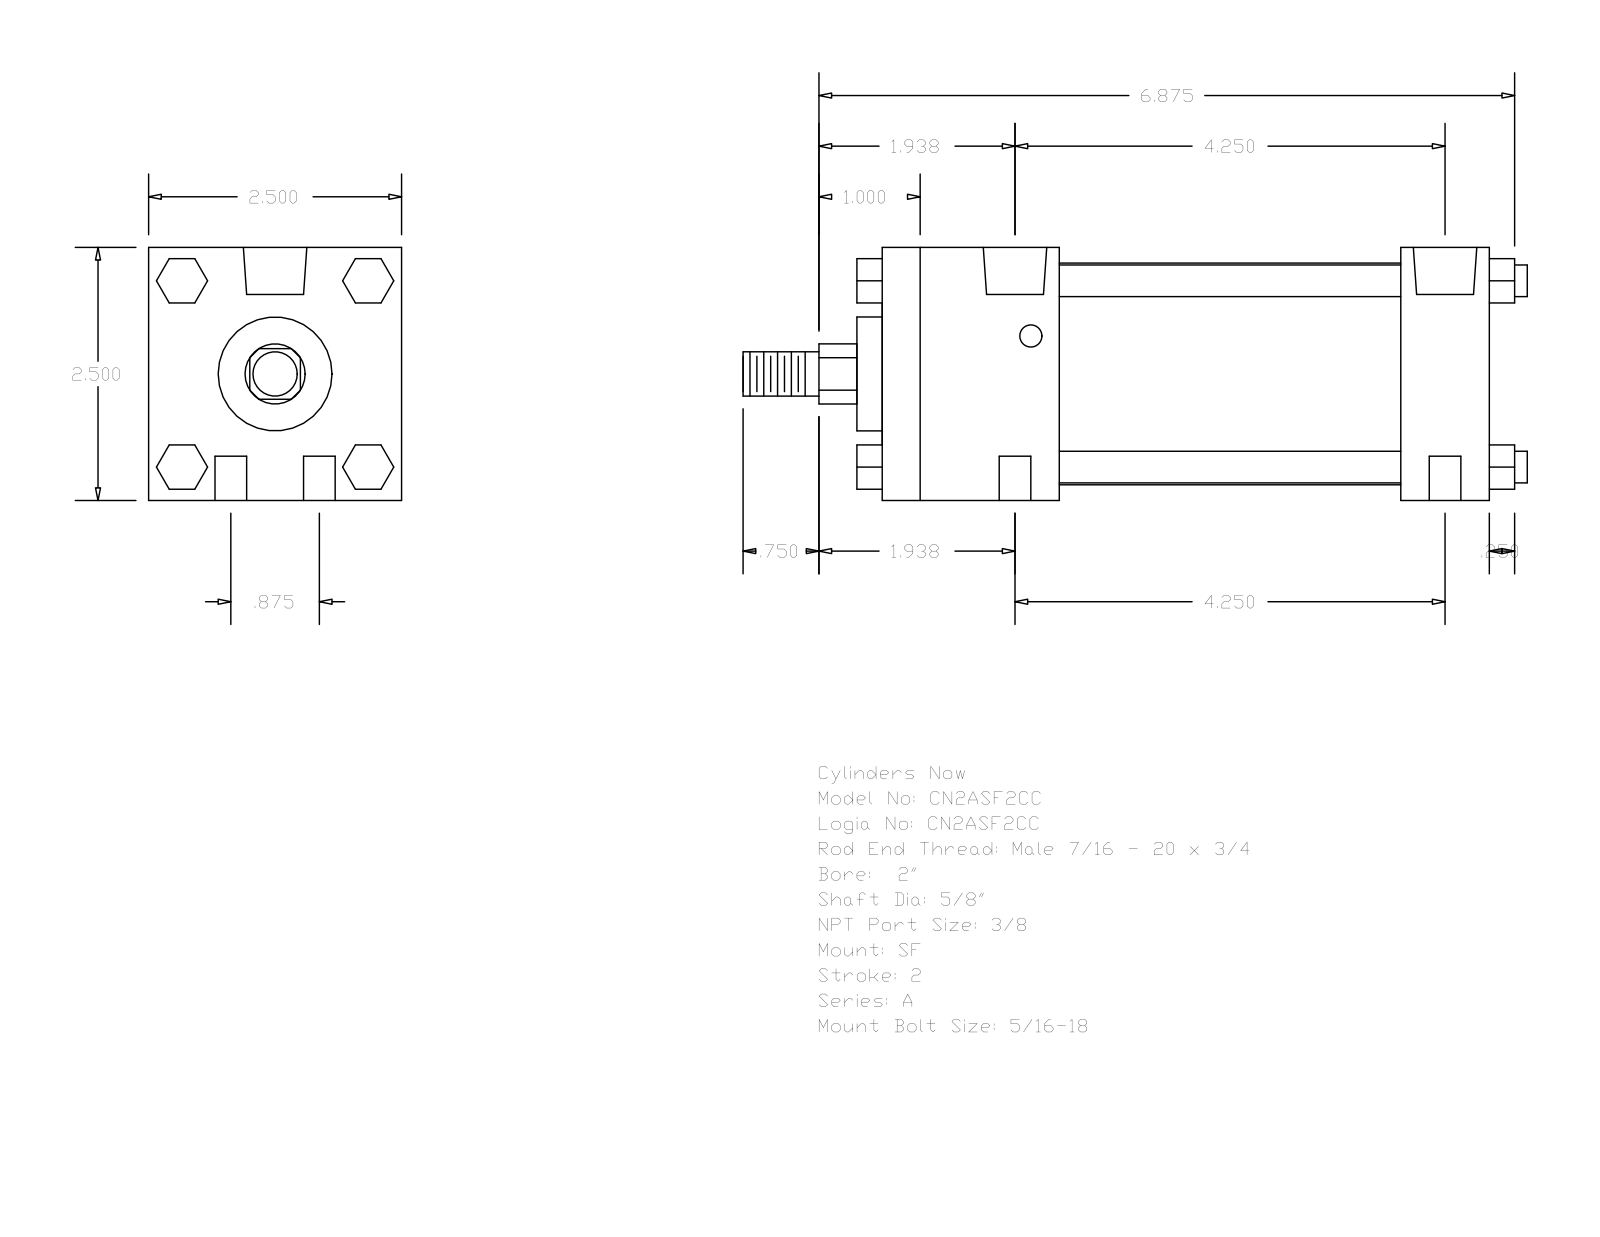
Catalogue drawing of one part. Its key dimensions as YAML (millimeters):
part_name: "A_SF__0200_0.625"
step_written_by: "GSSL Pune (CONFIG_CONTROL_DESIGN)"
units: millimeters
bodies: {solids: 0, faces: 124, planar: 94, cylindrical: 30, other: 0}
overall_size: [196.85, 63.5, 63.5]
round_holes:
  - {diameter: 7.94, count: 4}
  - {diameter: 5.56, count: 2}
  - {diameter: 15.93, count: 2}
round_bosses_or_shafts:
  - {diameter: 7.94, count: 4}
  - {diameter: 55.63, count: 1}
  - {diameter: 28.57, count: 1}
  - {diameter: 15.88, count: 1}
  - {diameter: 11.11, count: 1}
partial_cylinders:
  - {radius: 7.54, count: 1}
face_to_face_distances: [63.5, 152.4, 130.17, 22.23, 44.45, 85.72, 107.95, 50.8, 6.35, 136.52]
hole_center_spacings: [11.11, 108.52, 107.95, 22.22, 110.21, 100]
